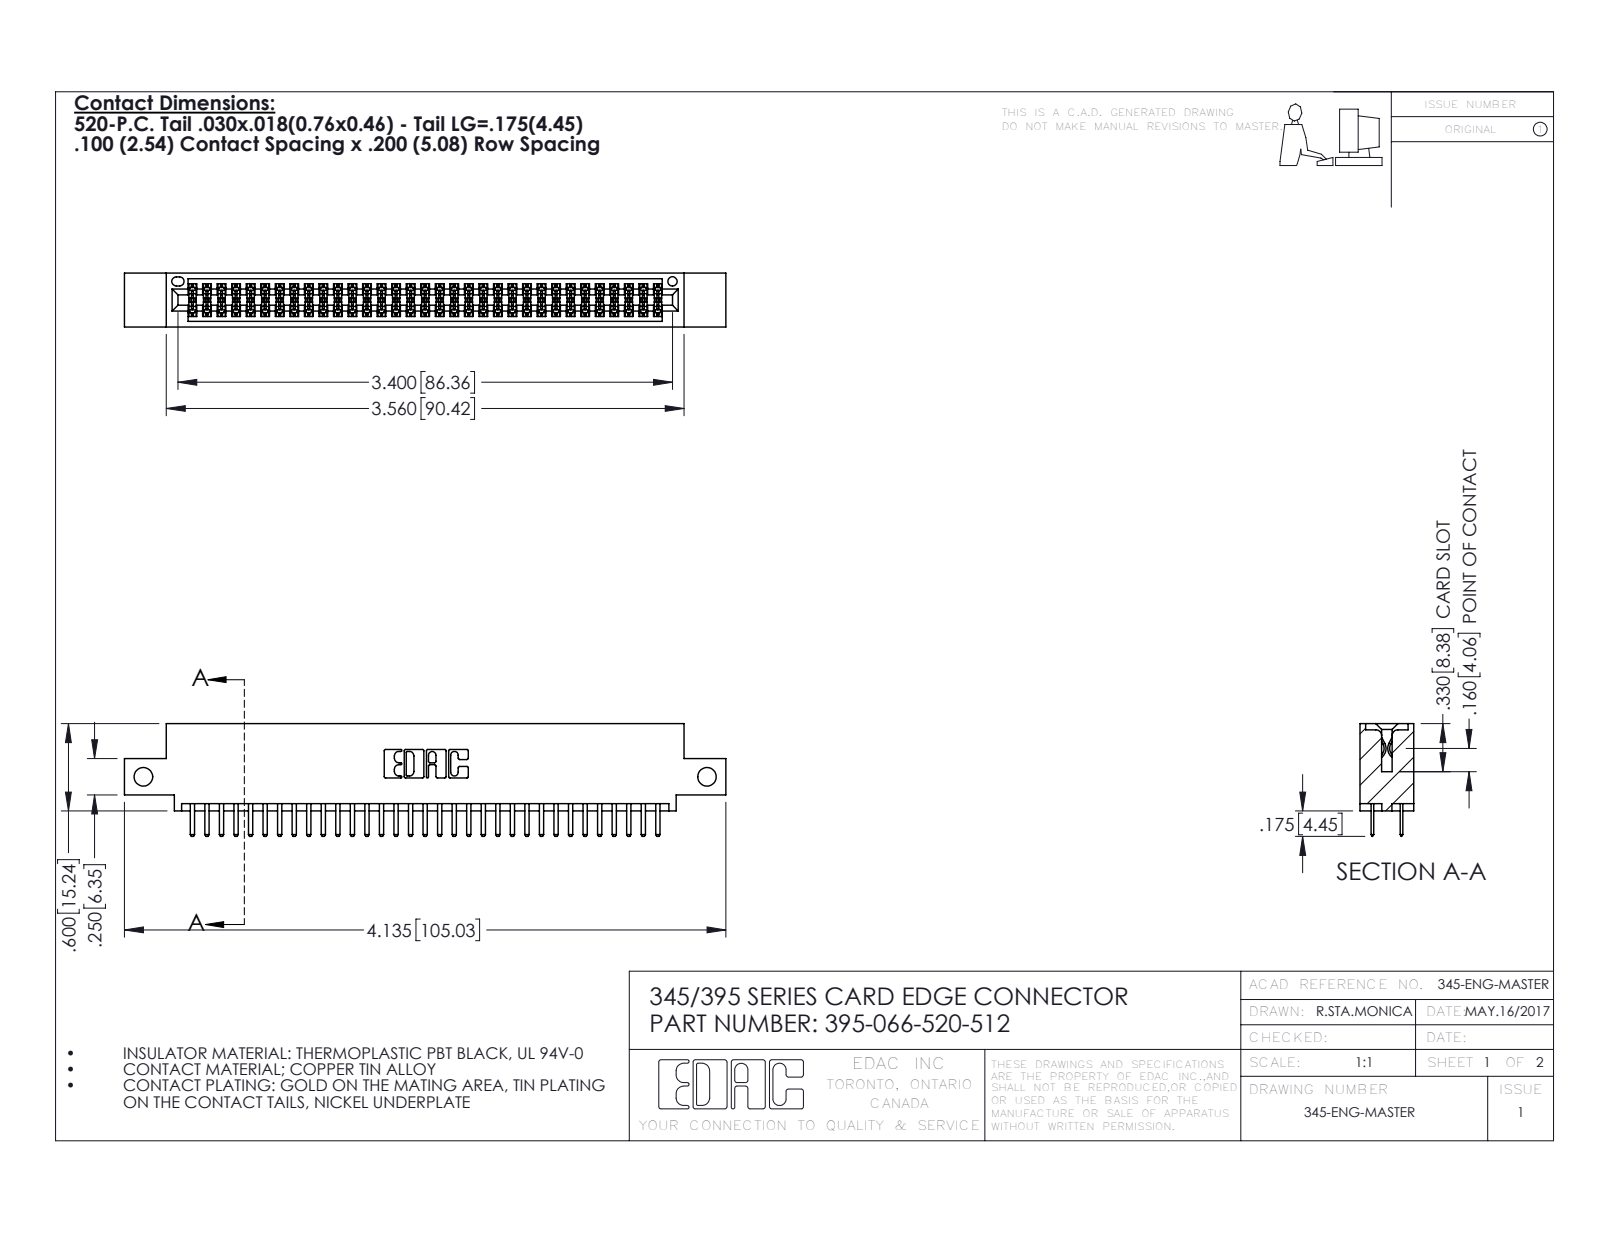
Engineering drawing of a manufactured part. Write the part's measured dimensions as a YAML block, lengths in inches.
part_name: "345-292-001_345-293-120; 395-066-520-512; 345 Part_0.110 Offset - Side Mount"
step_written_by: "SolidWorks 2016 (CONFIG_CONTROL_DESIGN)"
units: inches
bodies: {solids: 67, faces: 3694, planar: 2394, cylindrical: 1300, other: 0}
overall_size: [4.135, 0.775, 0.37]
volume: 0.606
surface_area: 22.32
round_holes:
  - {diameter: 0.128, count: 2}
  - {diameter: 0.064, count: 1}
partial_cylinders:
  - {radius: 0.006, count: 99}
  - {radius: 0.01, count: 70}
  - {radius: 0.01, count: 22}
  - {radius: 0.007, count: 6}
  - {radius: 0.031, count: 6}
  - {radius: 0.026, count: 3}
  - {radius: 0.014, count: 2}
  - {radius: 0.019, count: 2}
face_to_face_distances: [0.298, 0.072, 0.2, 0.37, 0.098, 0.272, 0.025, 0.225, 0.022, 0.072]
hole_center_spacings: [3.875]
